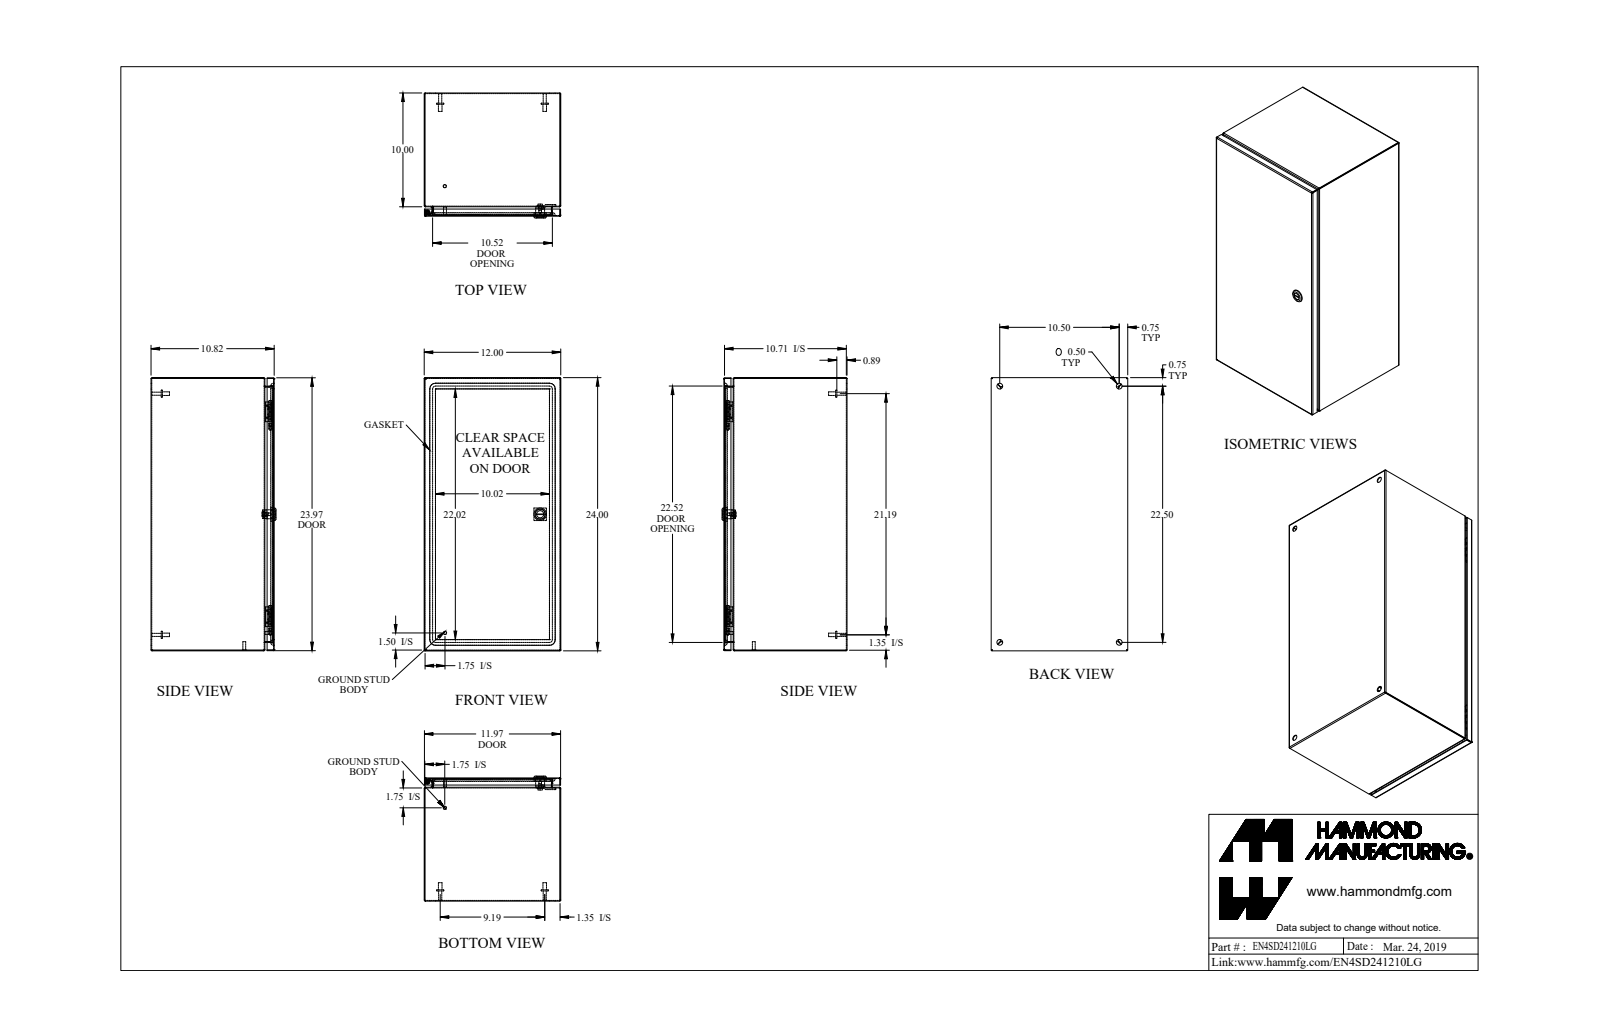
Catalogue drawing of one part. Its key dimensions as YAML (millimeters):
part_name: "EN4SD241210LG_Default"
step_written_by: "SolidWorks 2019 (CONFIG_CONTROL_DESIGN)"
units: millimeters
bodies: {solids: 21, faces: 634, planar: 285, cylindrical: 213, other: 136}
overall_size: [609.6, 304.8, 278.9]
volume: 1458000
surface_area: 1955000
round_holes:
  - {diameter: 12.7, count: 4}
  - {diameter: 4.4, count: 1}
  - {diameter: 5.9, count: 1}
  - {diameter: 6.1, count: 1}
  - {diameter: 6.1, count: 1}
  - {diameter: 15.9, count: 1}
  - {diameter: 19.9, count: 1}
round_bosses_or_shafts:
  - {diameter: 15.9, count: 4}
  - {diameter: 8, count: 4}
  - {diameter: 6.9, count: 4}
  - {diameter: 7.1, count: 2}
  - {diameter: 6.4, count: 2}
  - {diameter: 27.9, count: 1}
  - {diameter: 13.3, count: 1}
  - {diameter: 11.6, count: 1}
partial_cylinders:
  - {radius: 0.7, count: 21}
  - {radius: 2.2, count: 21}
  - {radius: 6.4, count: 16}
  - {radius: 482.6, count: 8}
  - {radius: 0.2, count: 4}
  - {radius: 1.6, count: 4}
  - {radius: 12.7, count: 4}
  - {radius: 3.2, count: 2}
face_to_face_distances: [1.4, 273.4, 303.4, 272, 274.9, 301.9, 304.8, 608.2, 606.7, 609.6]
hole_center_spacings: [266.7, 571.5, 630.7, 287, 287, 373, 373]
